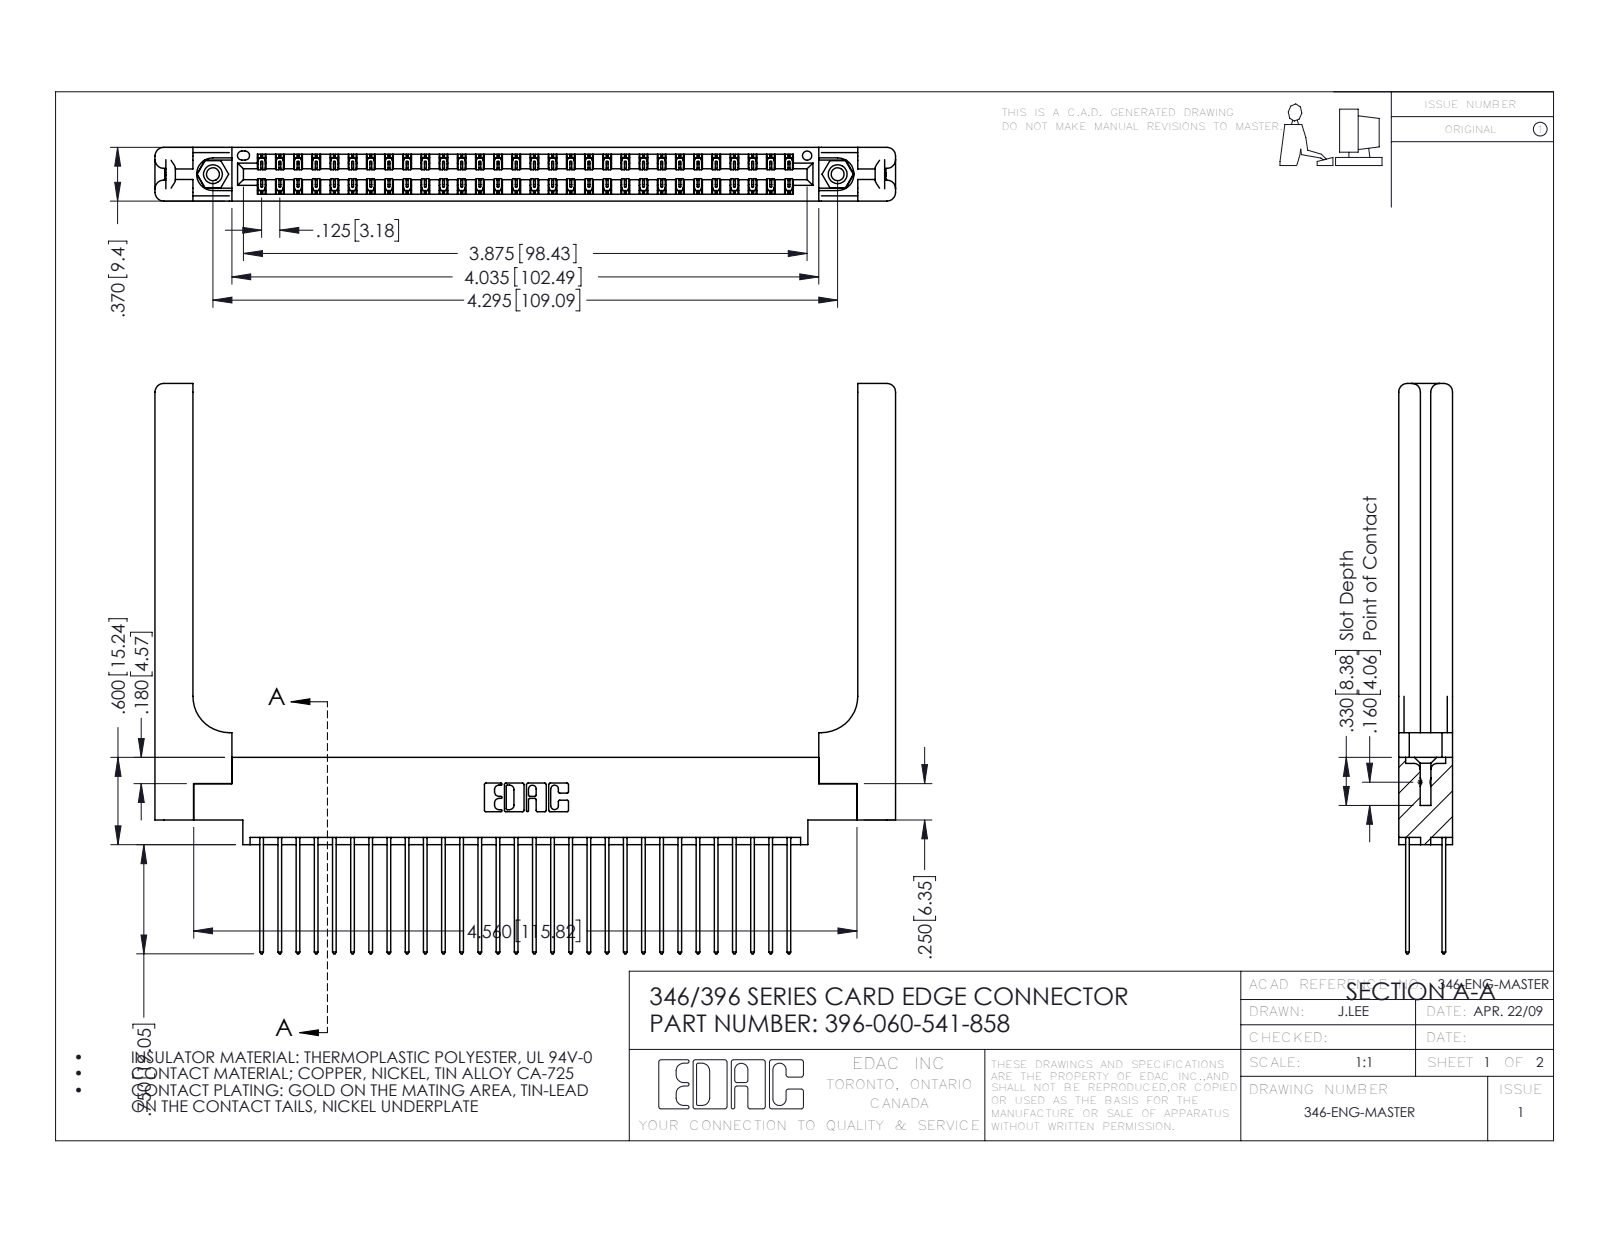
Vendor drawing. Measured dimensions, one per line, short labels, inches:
name: 345-292-001_345-293-141; 346-220-058_345-220-058; 396-060-541-858; 346 Part_0.170 Offset - 0.156 Dia-TH (+1 more)
written by: SolidWorks 2016 (CONFIG_CONTROL_DESIGN)
unit: in
bodies: 65 solids, 3502 faces (2328 planar, 1114 cylindrical, 60 other)
size: 5.091 × 3.92 × 0.37
volume: 1.233 in³; area: 37.32 in²
holes: 2× ⌀0.089, 2× ⌀0.125, 2× ⌀0.156, 1× ⌀0.064
bosses: 2× ⌀0.155
rounds: 90× R0.006, 60× R0.01, 22× R0.01, 16× R0.06, 6× R0.007, 6× R0.031, 3× R0.026, 2× R0.014
face distances: 0.048, 0.322, 0.072, 0.37, 0.25, 0.025, 0.298, 0.148, 0.15, 0.275
hole spacings: 0.246, 4.087, 4.295
